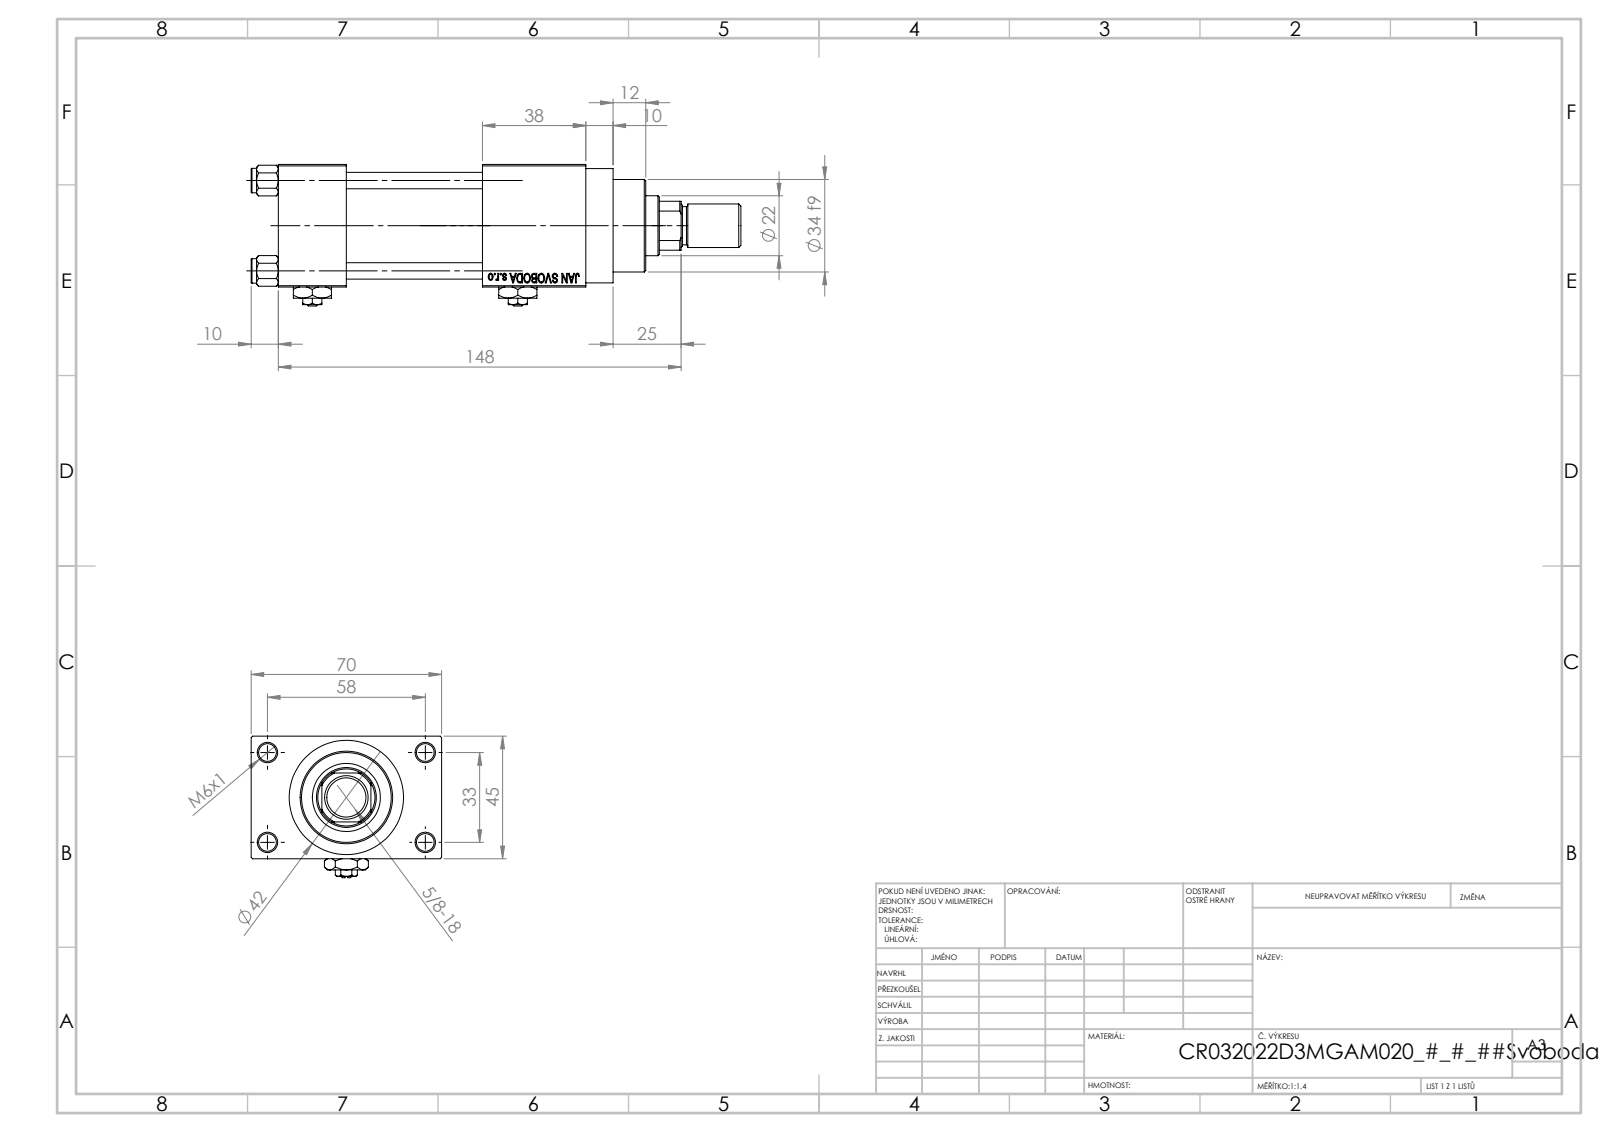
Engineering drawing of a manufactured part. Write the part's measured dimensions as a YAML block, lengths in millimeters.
part_name: "NUT_M5_D; Zatka_pro_OIL_PORT; V215CR_VCP_D; V215CR_D_TYCINKA (+3 more)"
step_written_by: "SolidWorks 2019 (CONFIG_CONTROL_DESIGN)"
units: millimeters
bodies: {solids: 14, faces: 1216, planar: 546, cylindrical: 104, other: 566}
overall_size: [180, 70, 52]
volume: 247677
surface_area: 82741
round_holes:
  - {diameter: 6, count: 4}
  - {diameter: 6.5, count: 4}
  - {diameter: 7, count: 2}
  - {diameter: 13.16, count: 2}
  - {diameter: 20, count: 2}
  - {diameter: 10.5, count: 1}
  - {diameter: 22, count: 1}
  - {diameter: 24, count: 1}
  - {diameter: 25, count: 1}
  - {diameter: 32, count: 1}
  - {diameter: 33, count: 1}
round_bosses_or_shafts:
  - {diameter: 9, count: 4}
  - {diameter: 42, count: 1}
  - {diameter: 38, count: 1}
  - {diameter: 34, count: 1}
  - {diameter: 16, count: 1}
  - {diameter: 14, count: 1}
partial_cylinders:
  - {radius: 10.5, count: 1}
face_to_face_distances: [45, 25, 12.5, 57.5, 50, 75, 88, 70, 38, 113]
hole_center_spacings: [12.4, 23.48, 33.2, 33.37, 35.35, 45.6, 56.35, 33]
